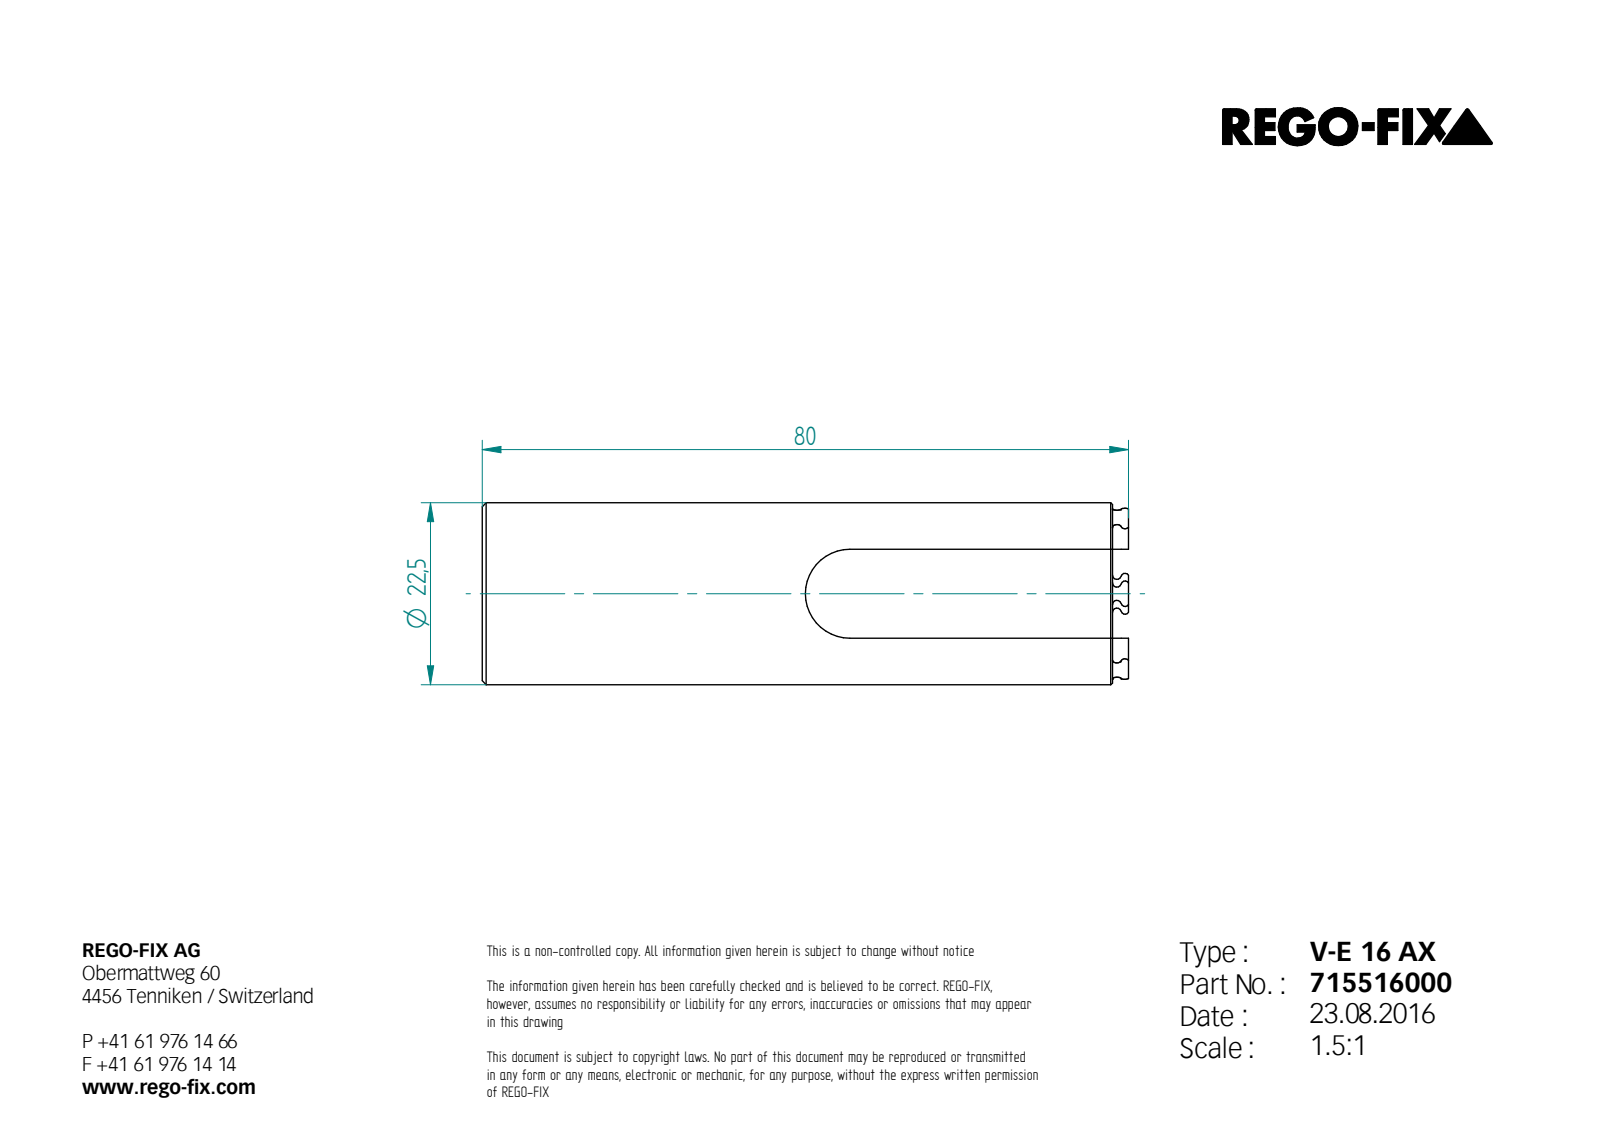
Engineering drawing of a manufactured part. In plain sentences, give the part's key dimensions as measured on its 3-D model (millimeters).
Its 3-D file was written by "Unknown (AUTOMOTIVE_DESIGN)". It is 1 solid with 60 faces: 22 planar, 17 cylindrical and 21 other. Overall it measures 80 by 22.5 by 22.5 millimeters. Its volume is 20 106 cubic millimeters and its surface area 8 744 square millimeters. Round holes: 1 of diameter 12.8. Round bosses or shafts: 1 of diameter 22.5. Partial cylindrical surfaces (rounded edges, fillets, slot ends): 1 of radius 3.55, 1 of radius 5.5, 1 of radius 6.6, 1 of radius 11.05. The main face-to-face distances are 11, 78, 6.55, 80, 2, 8.77, 2.23, 2.22, 8.78, 8.8.
